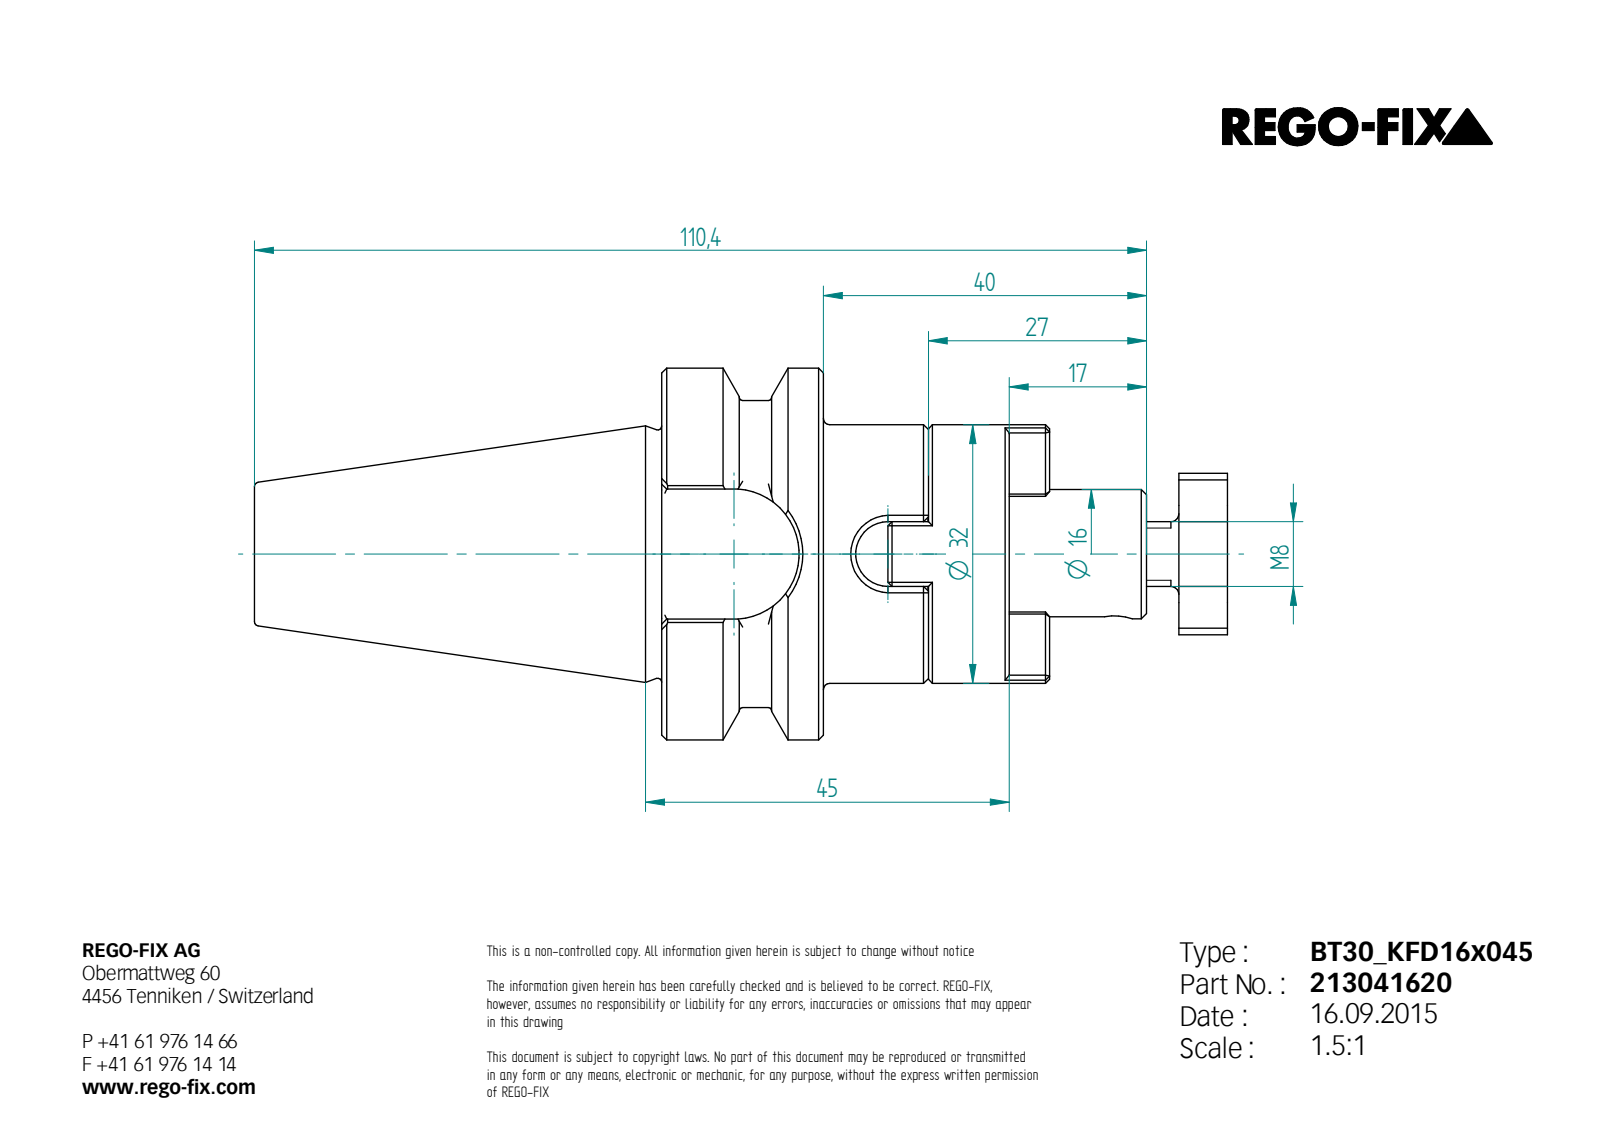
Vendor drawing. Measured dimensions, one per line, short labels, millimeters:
written by: Unknown (AUTOMOTIVE_DESIGN)
unit: mm
bodies: 3 solids, 217 faces (120 planar, 39 cylindrical, 58 other)
size: 120.4 × 46 × 46
volume: 69 579 mm³; area: 20 530 mm²
holes: 1× ⌀6.65, 1× ⌀8.4, 1× ⌀10.11, 1× ⌀12.5, 1× ⌀16
bosses: 1× ⌀46, 1× ⌀32, 1× ⌀15.6, 1× ⌀8
rounds: 8× R0.5, 6× R2, 1× R4, 1× R8.05, 1× R10, 1× R19
face distances: 20, 13, 33, 10, 43, 23, 8, 27, 6, 70
